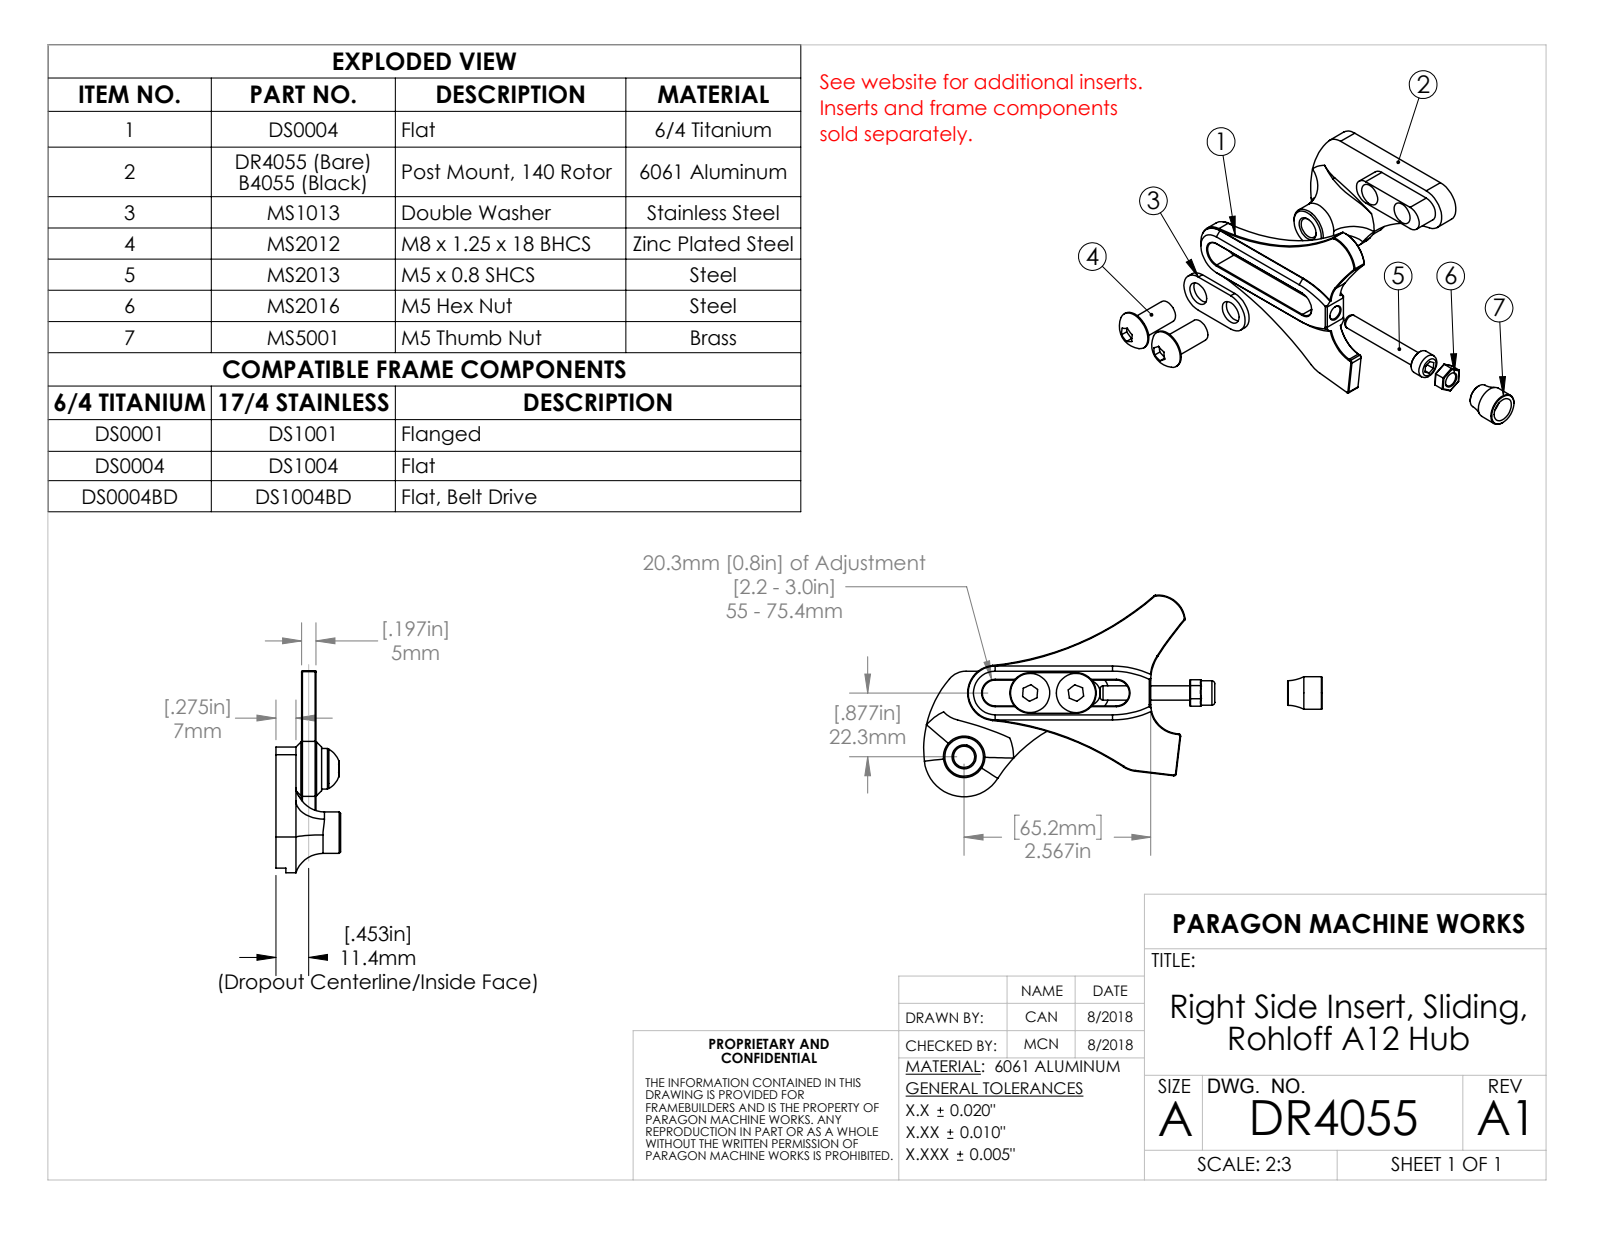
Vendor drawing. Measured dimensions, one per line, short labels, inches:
name: DR4055_Flat; DS0004; DR4055; MS1013 (+4 more)
written by: SolidWorks 2018 (AUTOMOTIVE_DESIGN)
unit: in
bodies: 8 solids, 249 faces (84 planar, 87 cylindrical, 78 other)
size: 6.136 × 5.083 × 2.772
volume: 1.899 in³; area: 27.41 in²
holes: 2× ⌀0.312, 2× ⌀0.327, 1× ⌀0.197, 1× ⌀0.291, 1× ⌀0.335
bosses: 2× ⌀0.539, 2× ⌀0.315, 1× ⌀0.571, 1× ⌀0.449
rounds: 12× R0.01, 4× R0.03, 4× R0.178, 2× R0.28, 2× R0.3, 2× R0.4, 2× R1.27, 2× R4
face distances: 0.276, 2.586, 2.507, 0.197, 2.783, 0.079, 2.311, 0.138, 1.106, 0.83
hole spacings: 0.63, 1.262, 1.77
